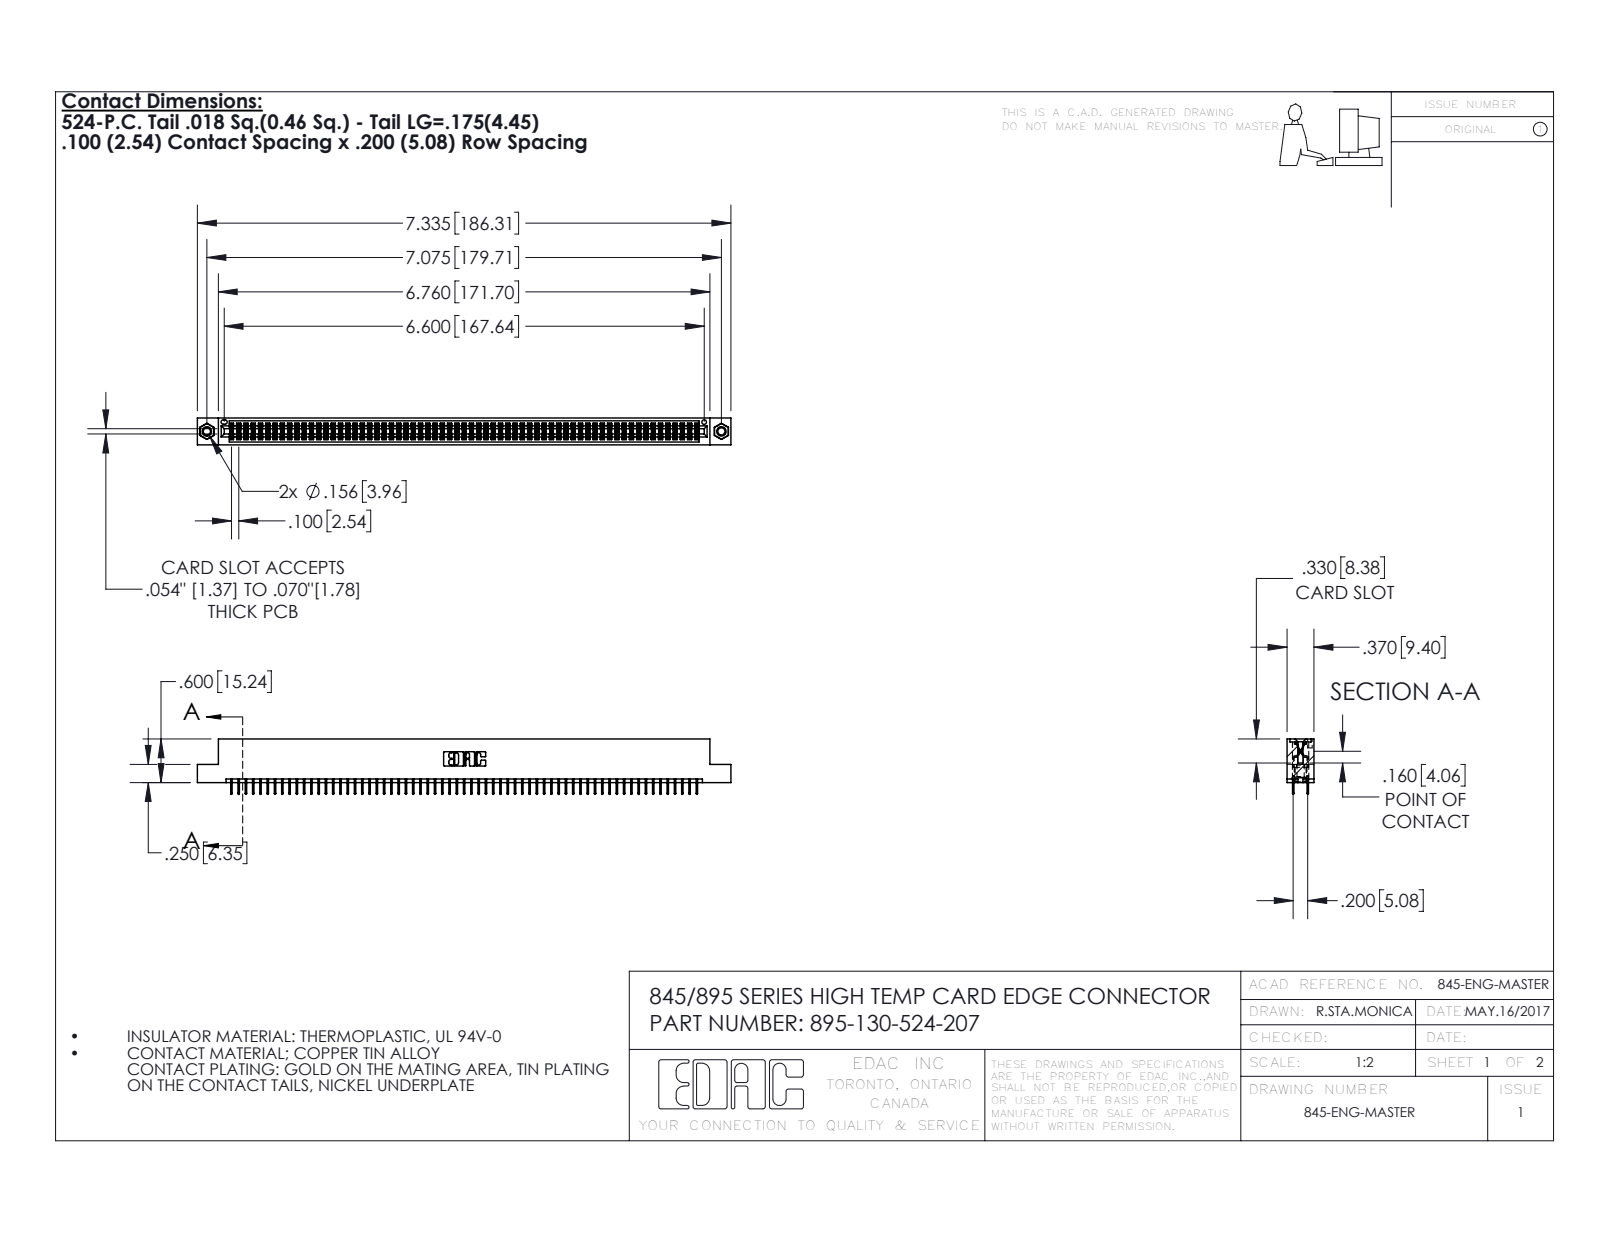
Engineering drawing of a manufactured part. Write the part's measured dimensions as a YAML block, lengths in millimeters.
part_name: "395-130-524-207; 345-250-001_345-250-005-103; 345 Part_Flush Mounting Lugs - 0.156 Dia-TI; 345-292-001_345-293-124"
step_written_by: "SolidWorks 2016 (CONFIG_CONTROL_DESIGN)"
units: millimeters
bodies: {solids: 133, faces: 7206, planar: 5182, cylindrical: 2008, other: 16}
overall_size: [186.3, 19.4, 9.4]
volume: 18110
surface_area: 26710
round_holes:
  - {diameter: 2.5, count: 2}
  - {diameter: 3.2, count: 2}
  - {diameter: 4, count: 2}
  - {diameter: 1.6, count: 1}
round_bosses_or_shafts:
  - {diameter: 3.9, count: 2}
partial_cylinders:
  - {radius: 0.2, count: 196}
  - {radius: 0.3, count: 22}
  - {radius: 0.2, count: 6}
  - {radius: 0.8, count: 6}
  - {radius: 0.7, count: 3}
  - {radius: 0.4, count: 2}
  - {radius: 0.5, count: 2}
  - {radius: 0.6, count: 2}
face_to_face_distances: [1.8, 7.6, 5.1, 9.4, 2.5, 6.9, 0.6, 5.7, 1.8, 4.4]
hole_center_spacings: [6.9, 173.7, 179.7]
